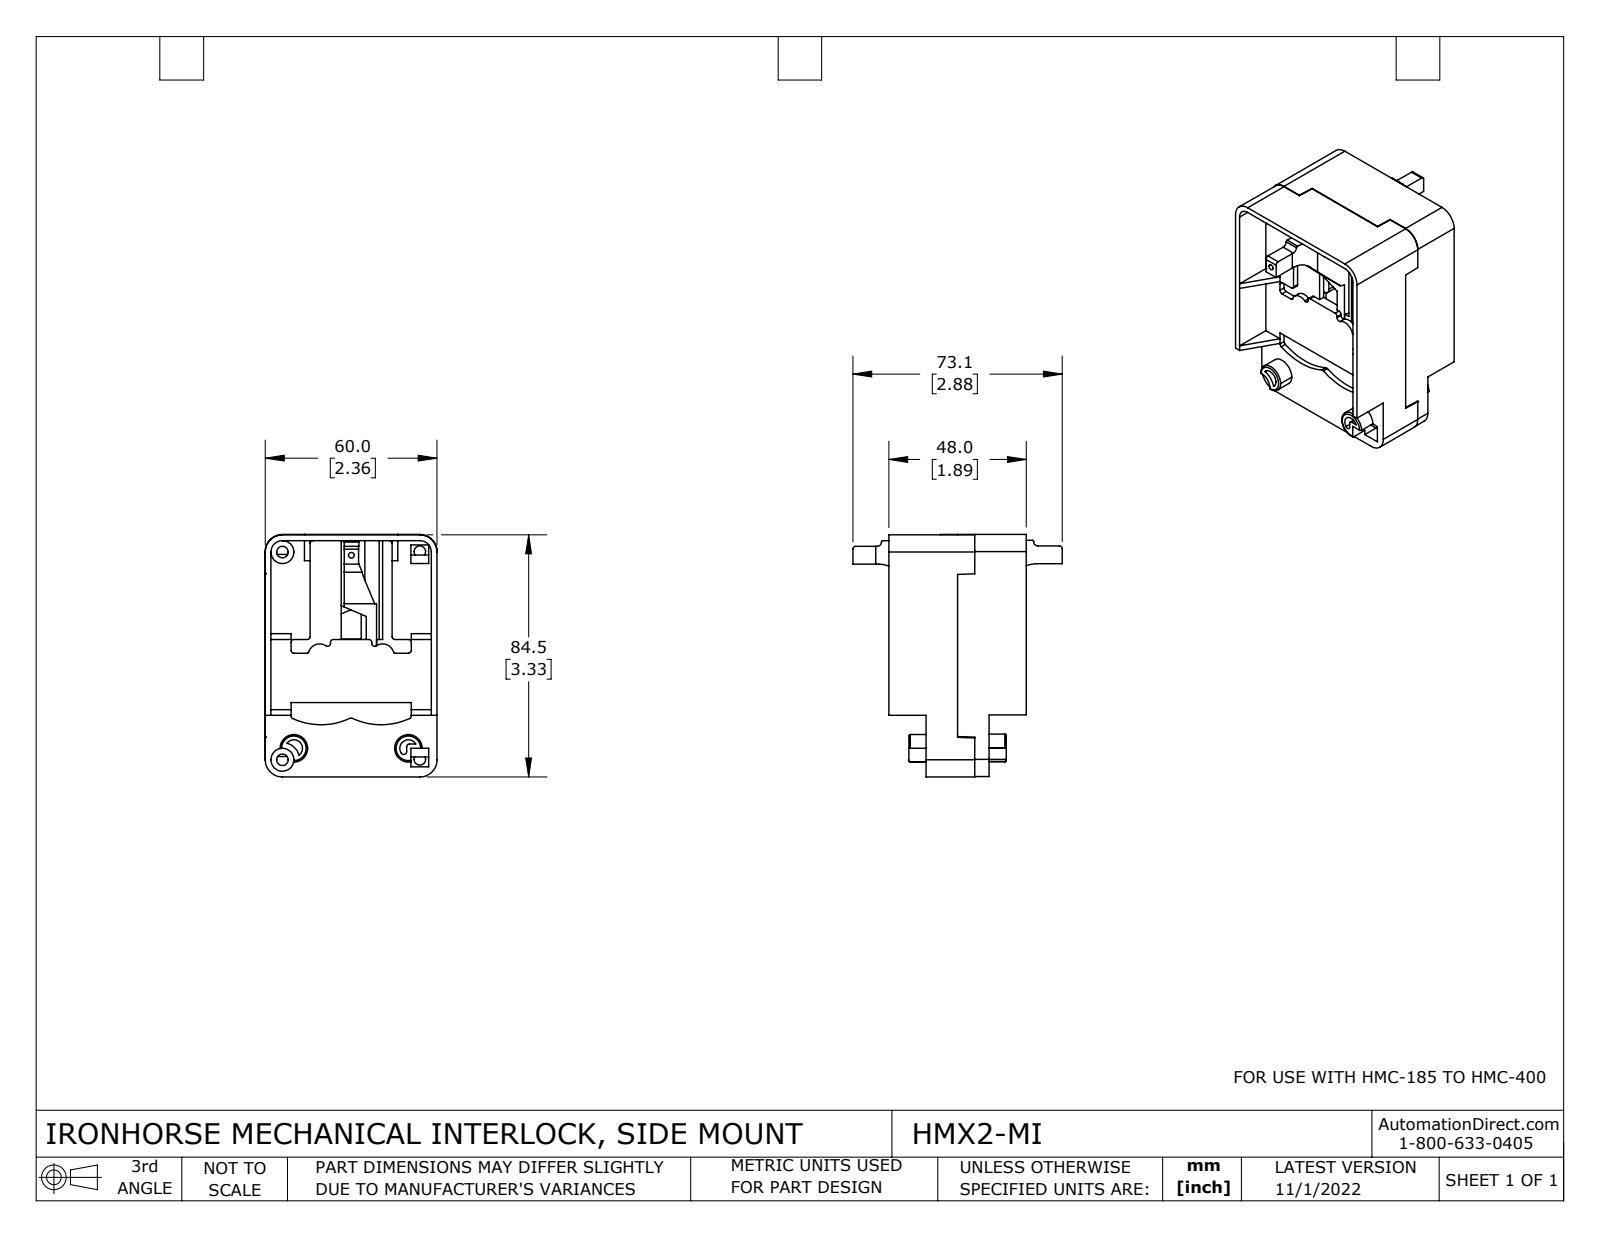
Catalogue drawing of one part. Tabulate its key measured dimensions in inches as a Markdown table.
| quantity | value |
| --- | --- |
| part name | HMX2-MI |
| STEP written by | SolidWorks 2021 (CONFIG_CONTROL_DESIGN) |
| units | inches |
| bodies | 1 solid, 374 faces (250 planar, 112 cylindrical, 12 other) |
| overall size | 3.333 × 2.88 × 2.363 |
| volume | 5.504 in³ |
| surface area | 65.43 in² |
| round holes (diameter × count) | 0.157 × 4, 0.315 × 4, 0.079 × 2 |
| partial cylindrical surfaces (radius × count) | 0.039 × 36, 0.079 × 8, 0.236 × 8, 0.02 × 6, 0.157 × 6, 0.118 × 4, 0.189 × 4, 0.945 × 4 |
| main face-to-face distances | 0.079, 0.709, 0.157, 0.539, 1.744, 0.866, 2.362, 2.283, 0.078, 1.823 |
| hole center spacings | 0.95, 1.889, 2.854, 2.967, 0.941, 0.942, 2.959, 2.97 |
